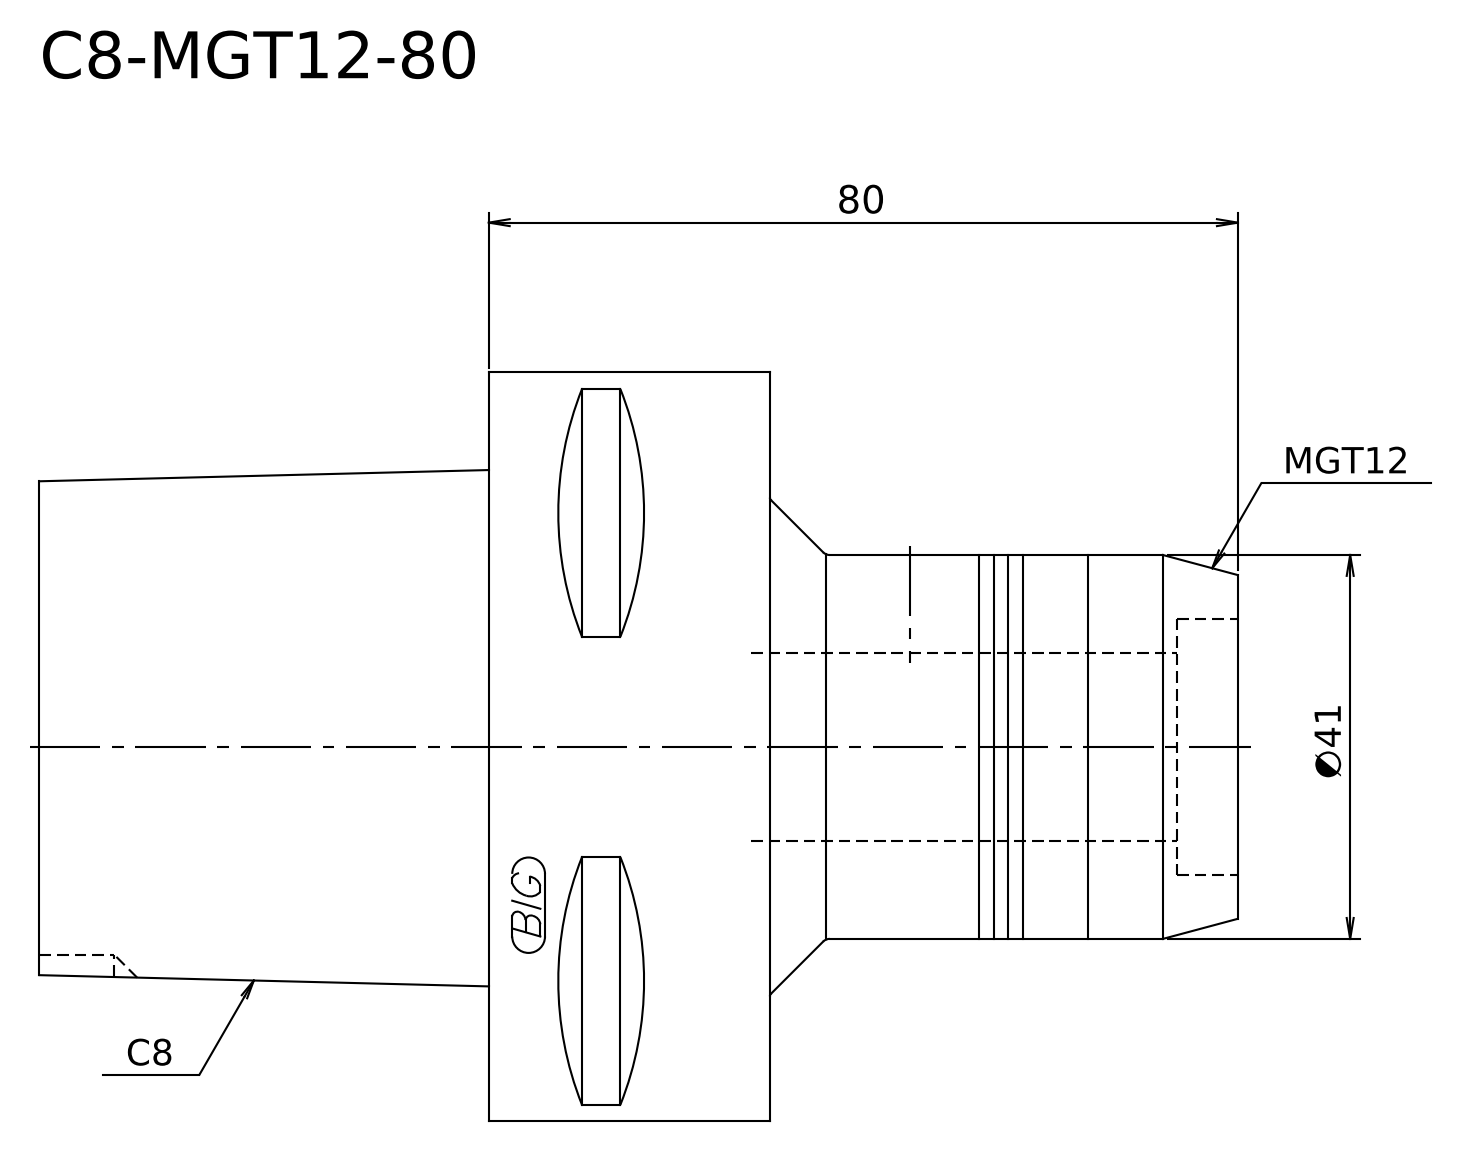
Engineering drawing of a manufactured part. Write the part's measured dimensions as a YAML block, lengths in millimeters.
step_written_by: "Kubotek KeyCreator V8.5.1 (14335) (CONFIG_CONTROL_DESIGN)"
units: millimeters
bodies: {solids: 1, faces: 9, planar: 4, cylindrical: 2, other: 3}
overall_size: [128, 79.98, 79.98]
volume: 324619
surface_area: 31275
round_bosses_or_shafts:
  - {diameter: 79.98, count: 1}
  - {diameter: 41, count: 1}
face_to_face_distances: [30, 78, 48, 50, 80, 128]
